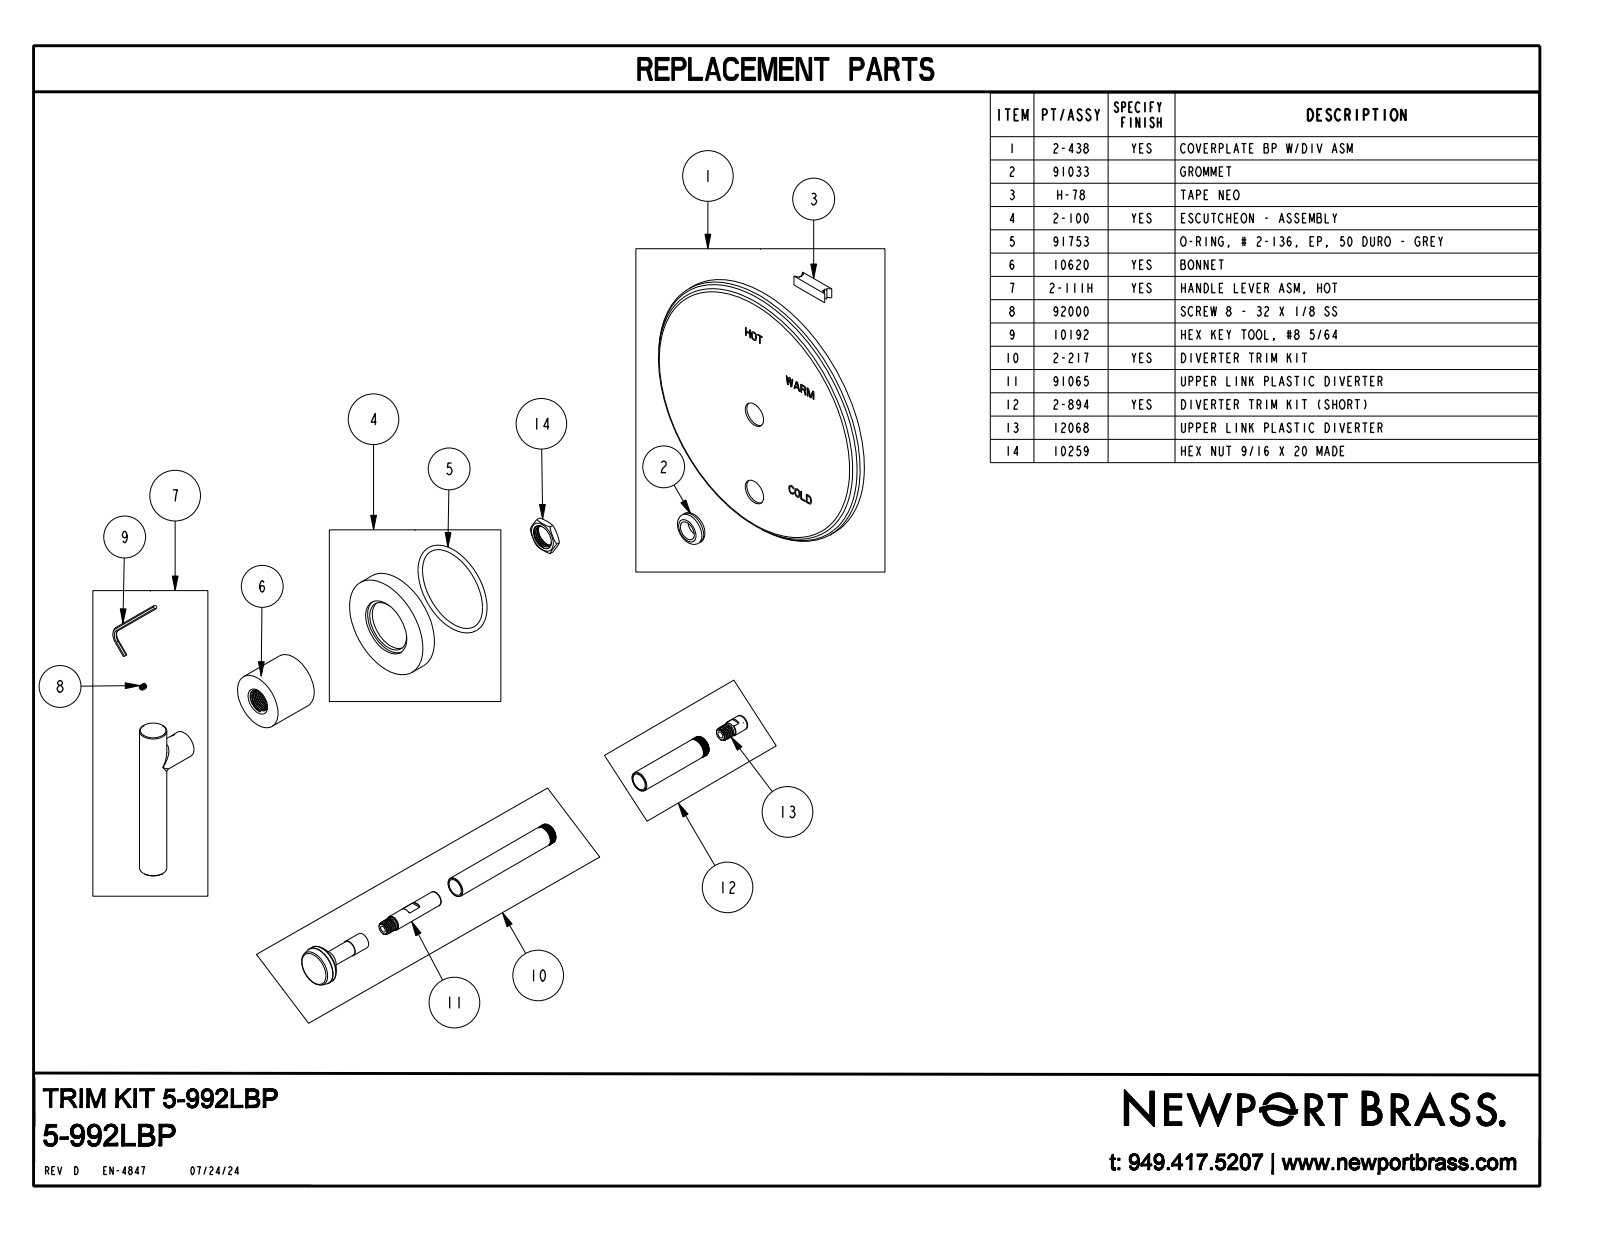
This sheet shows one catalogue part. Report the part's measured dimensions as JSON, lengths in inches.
{"part_name": "5-992LBP", "step_written_by": "CREO PARAMETRIC BY PTC INC, 2018400 (CONFIG_CONTROL_DESIGN)", "units": "inches", "bodies": {"solids": 1, "faces": 317, "planar": 270, "cylindrical": 19, "other": 28}, "overall_size": [6.5, 6.5, 3.139], "volume_in3": 15.1, "surface_area_in2": 90.75, "round_bosses_or_shafts": [[0.625, 2], [6.5, 1], [2.375, 1], [1.313, 1], [0.9, 1], [0.472, 1], [0.4, 1], [0.354, 1]], "face_to_face_distances": [0.313, 0.688, 0.375, 1.796, 1.483, 1.108, 1.66, 1.347, 0.972, 0.136]}
